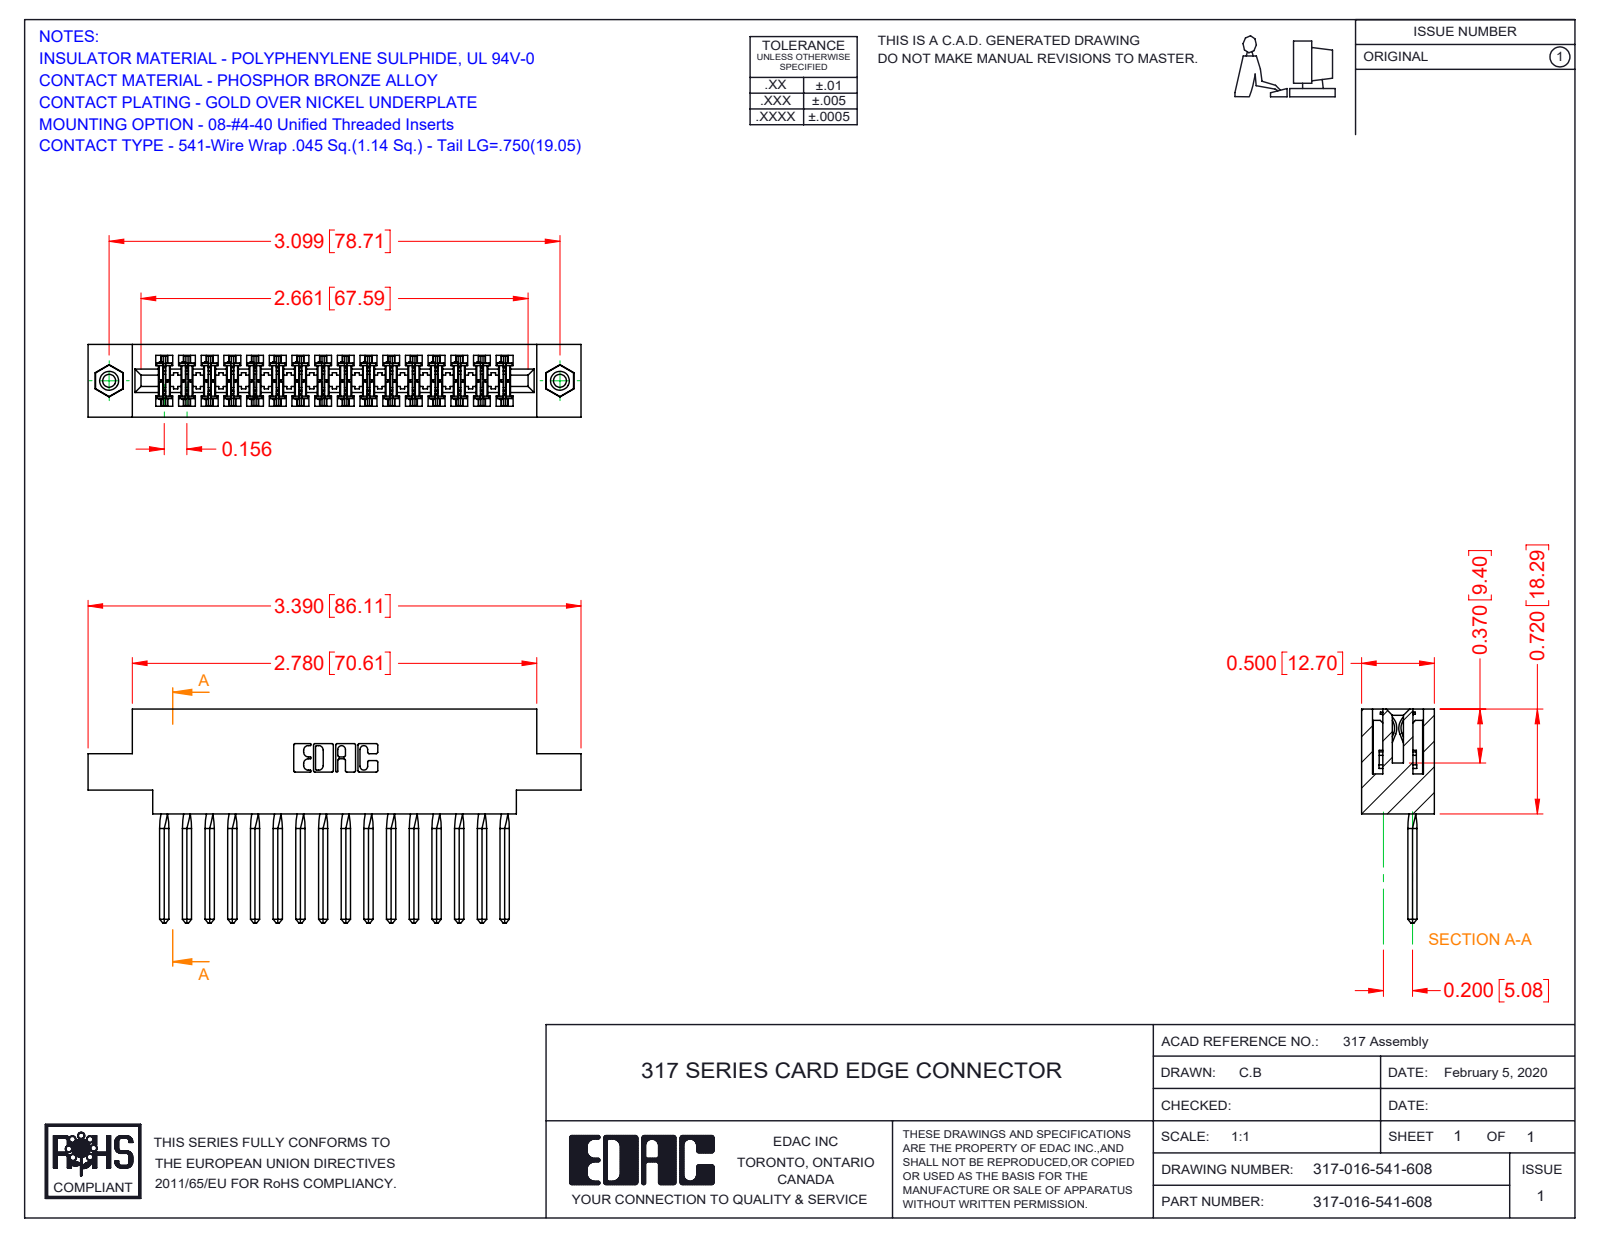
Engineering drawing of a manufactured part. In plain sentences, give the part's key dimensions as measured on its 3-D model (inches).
The part is named "317-016-541-678; 345-250-001_345-250-003-102; 317-290-002_541; 317 Part_.156 Dia - TI". Its 3-D file was written by "SolidWorks 2016 (CONFIG_CONTROL_DESIGN)". It is 19 solids with 2594 faces: 2074 planar, 440 cylindrical and 80 other. Overall it measures 3.39 by 1.47 by 0.5 inches. Its volume is 0.803 cubic inches and its surface area 27.51 square inches. Round holes: 2 of diameter 0.089, 2 of diameter 0.125, 2 of diameter 0.156. Round bosses or shafts: 2 of diameter 0.155. Partial cylindrical surfaces (rounded edges, fillets, slot ends): 32 of radius 0.015, 22 of radius 0.01, 6 of radius 0.007, 6 of radius 0.031, 3 of radius 0.026, 2 of radius 0.095, 2 of radius 0.1, 2 of radius 0.11. The main face-to-face distances are 0.5, 0.075, 0.425, 0.11, 0.35, 0.22, 0.195, 0.065, 0.136, 0.72. The hole center spacings are 3.099.
